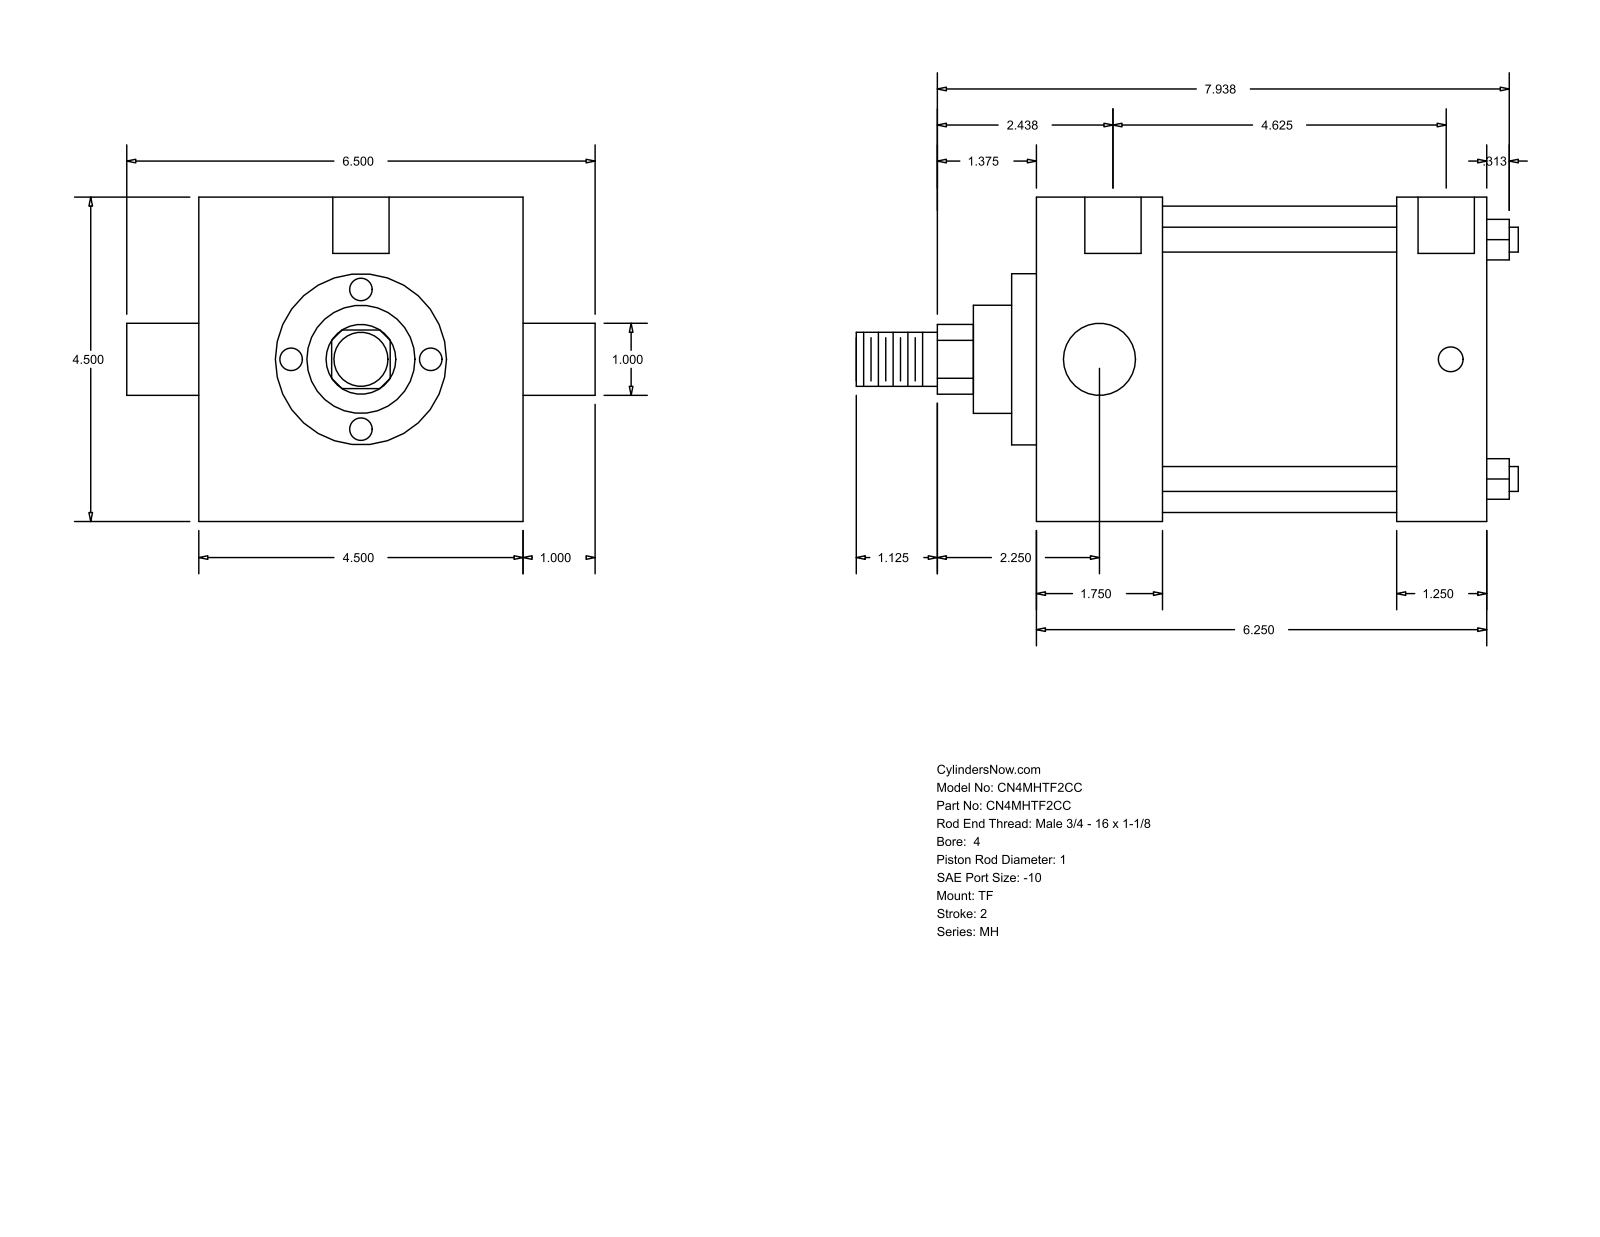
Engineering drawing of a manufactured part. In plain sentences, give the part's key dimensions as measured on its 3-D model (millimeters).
The part is named "MH_TF__0400_1". Its 3-D file was written by "GSSL Pune (CONFIG_CONTROL_DESIGN)". It is 0 solids with 86 faces: 61 planar, 25 cylindrical and 0 other. Overall it measures 233.36 by 165.1 by 114.3 millimeters. Round holes: 3 of diameter 8.73, 2 of diameter 19.84. Round bosses or shafts: 4 of diameter 8.76, 2 of diameter 25.4, 1 of diameter 107.95, 1 of diameter 60.33, 1 of diameter 38.1, 1 of diameter 19.05. Partial cylindrical surfaces (rounded edges, fillets, slot ends): 1 of radius 12.29. The main face-to-face distances are 114.3, 158.76, 44.46, 127.01, 82.55, 31.75, 8.73, 53.19, 135.74, 167.49. The hole center spacings are 1.58, 119.06, 117.48, 120.64.
